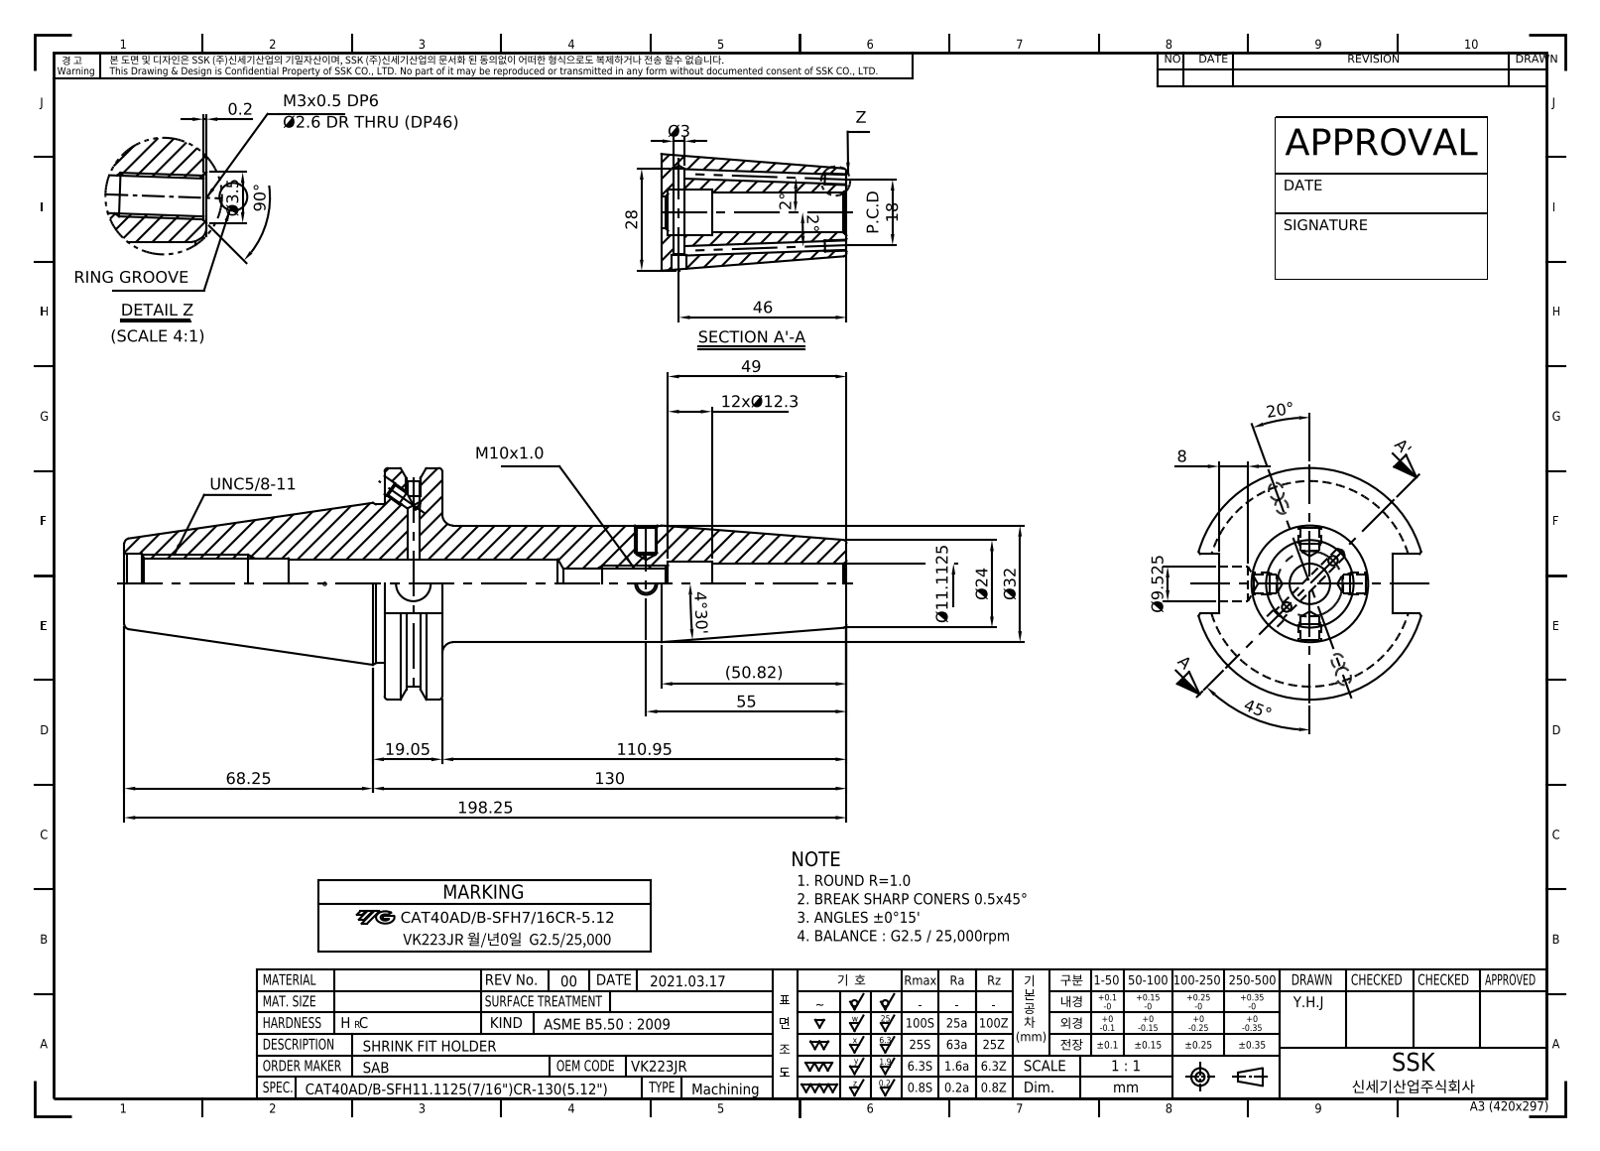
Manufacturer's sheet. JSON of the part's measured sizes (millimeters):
{"part_name": "LO-CAT40ADB-SFH11.1125CR-130", "step_written_by": "Autodesk Inventor 2022 (AUTOMOTIVE_DESIGN)", "units": "millimeters", "bodies": {"solids": 1, "faces": 91, "planar": 37, "cylindrical": 31, "other": 23}, "overall_size": [198.25, 63.5, 61.09], "volume_mm3": 169234, "surface_area_mm2": 35435, "round_holes": [[3.24, 4], [2.46, 2], [4, 2], [4.2, 2], [8.92, 1], [9.53, 1], [11.11, 1], [12.3, 1], [13, 1], [13.39, 1], [16.3, 1]], "round_bosses_or_shafts": [[63.5, 1], [43.6, 1], [32, 1]], "partial_cylinders_radius": [[28.15, 1]], "face_to_face_distances": [15.88, 126.83, 110.95, 47.6, 16.38, 71.42, 87.3, 198.25, 77.47, 6.05]}
